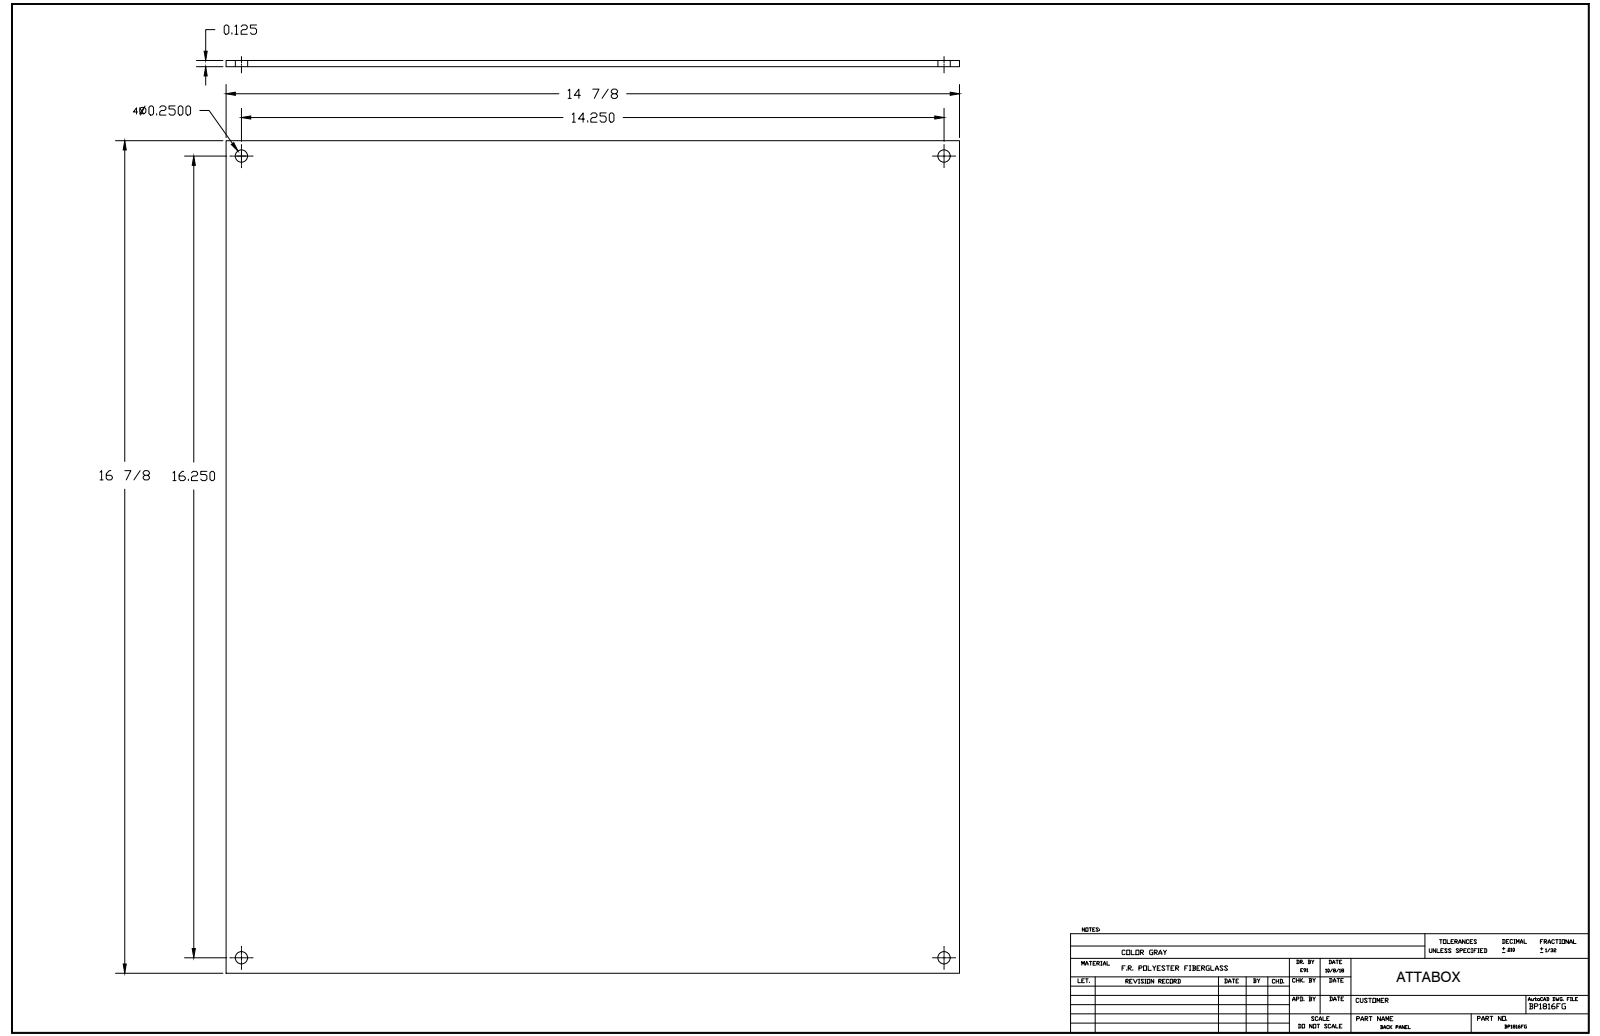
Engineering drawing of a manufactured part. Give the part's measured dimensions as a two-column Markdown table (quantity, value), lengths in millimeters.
| quantity | value |
| --- | --- |
| part name | BP1816FG_STP |
| STEP written by | Autodesk Inventor 2014 (AUTOMOTIVE_DESIGN) |
| units | millimeters |
| bodies | 1 solid, 10 faces (6 planar, 4 cylindrical, 0 other) |
| overall size | 428.62 × 377.82 × 3.17 |
| volume | 513 774 mm³ |
| surface area | 329 011 mm² |
| round holes (diameter × count) | 6.35 × 4 |
| main face-to-face distances | 3.17, 377.82, 428.62 |
| hole center spacings | 361.94, 412.76, 548.97 |
